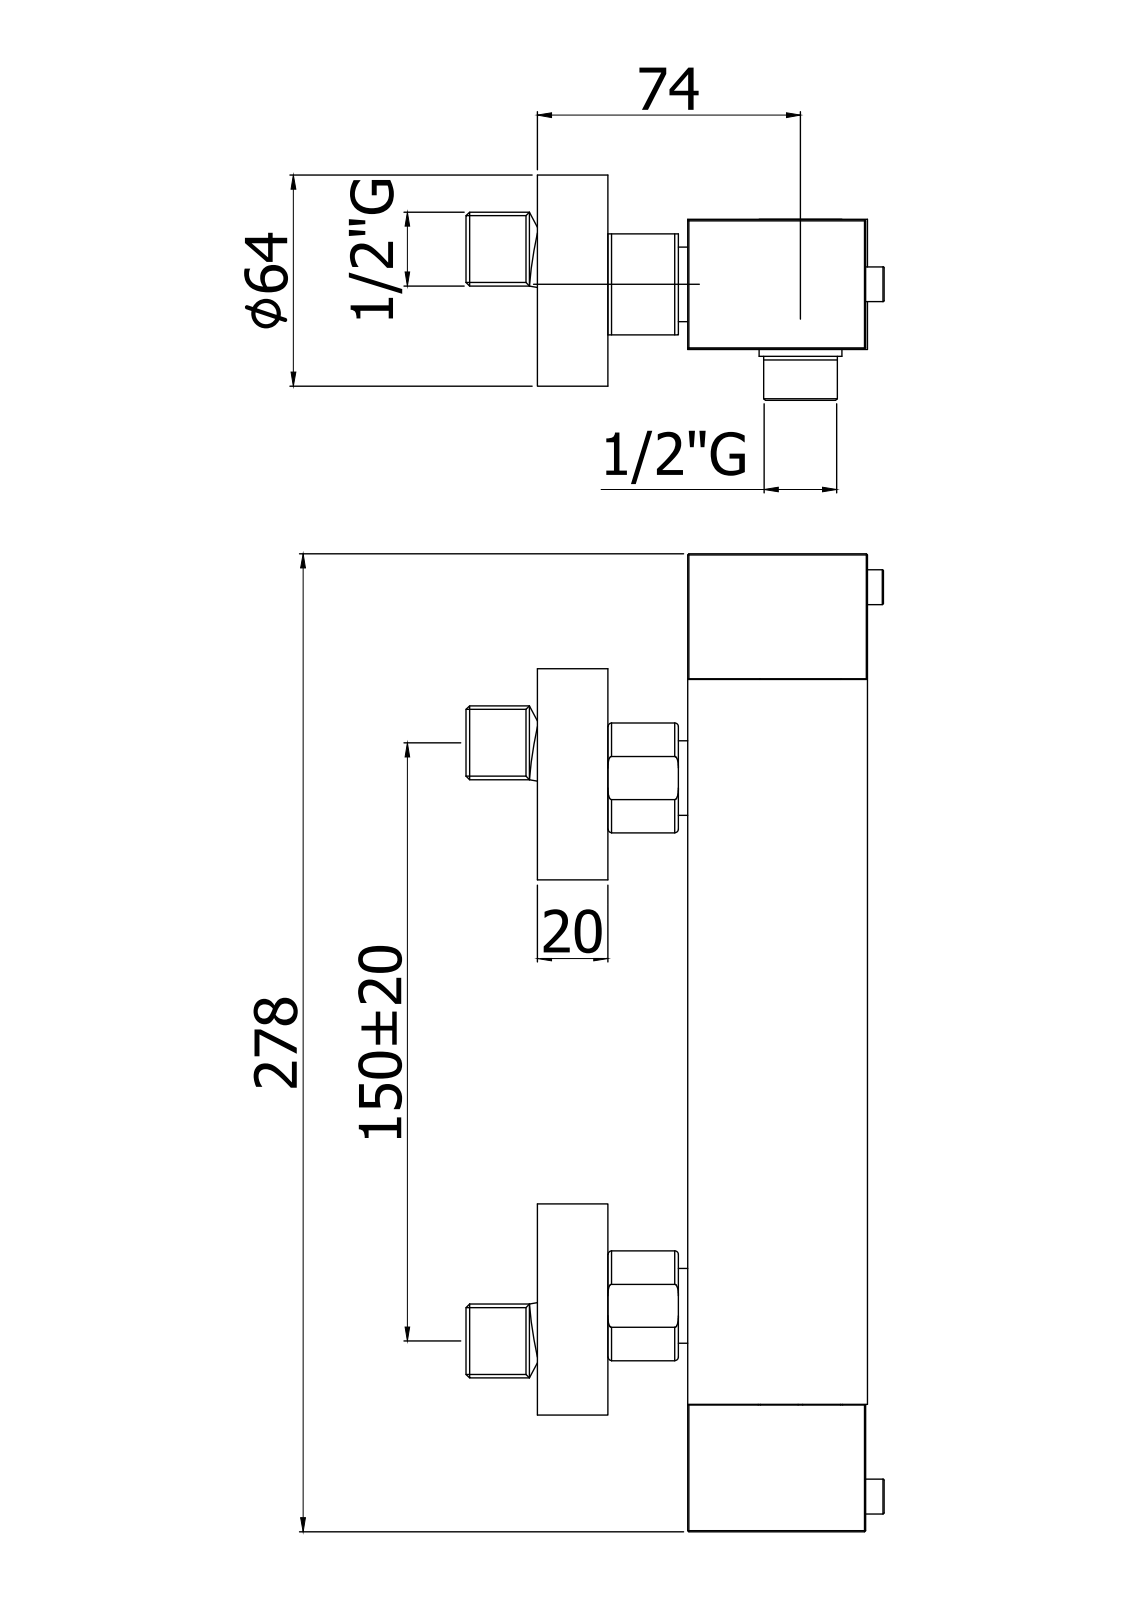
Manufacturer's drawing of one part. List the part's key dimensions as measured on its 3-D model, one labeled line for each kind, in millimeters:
Part name (STEP PRODUCT): LEQ268CR
STEP written by: CREO PARAMETRIC BY PTC INC, 2020044 (CONFIG_CONTROL_DESIGN)
Units: millimetres
Bodies: 4 solids, 352 faces (199 planar, 97 cylindrical, 56 other)
Overall size (bounding box): 278.55 × 99.25 × 65
Volume: 645 016 mm³ · Surface area: 94 539 mm²
Round holes (diameter × count): ⌀15.1 ×2, ⌀16 ×2, ⌀18 ×2, ⌀24.1 ×2, ⌀2.5 ×1, ⌀3 ×1, ⌀3.25 ×1, ⌀4 ×1, ⌀4.5 ×1, ⌀5.5 ×1, ⌀6 ×1, ⌀6.4 ×1
Round bosses / shafts (diameter × count): ⌀63.5 ×2, ⌀24 ×2, ⌀21.2 ×2, ⌀9.8 ×2, ⌀7.6 ×2, ⌀23 ×1, ⌀20.9 ×1, ⌀13 ×1
Partial cylindrical surfaces — rounded edges, fillets, slot ends (radius × count): R5 ×6, R1.75 ×2, R15.6 ×2, R4.82 ×1, R16.5 ×1
Main face-to-face distances: 37.5, 0.4, 37.1, 94.7, 20, 74.7, 43.7, 23.7, 51, 52
Hole centre spacings: 4, 14.05, 50.65, 54.65, 150, 200.65, 204.65
